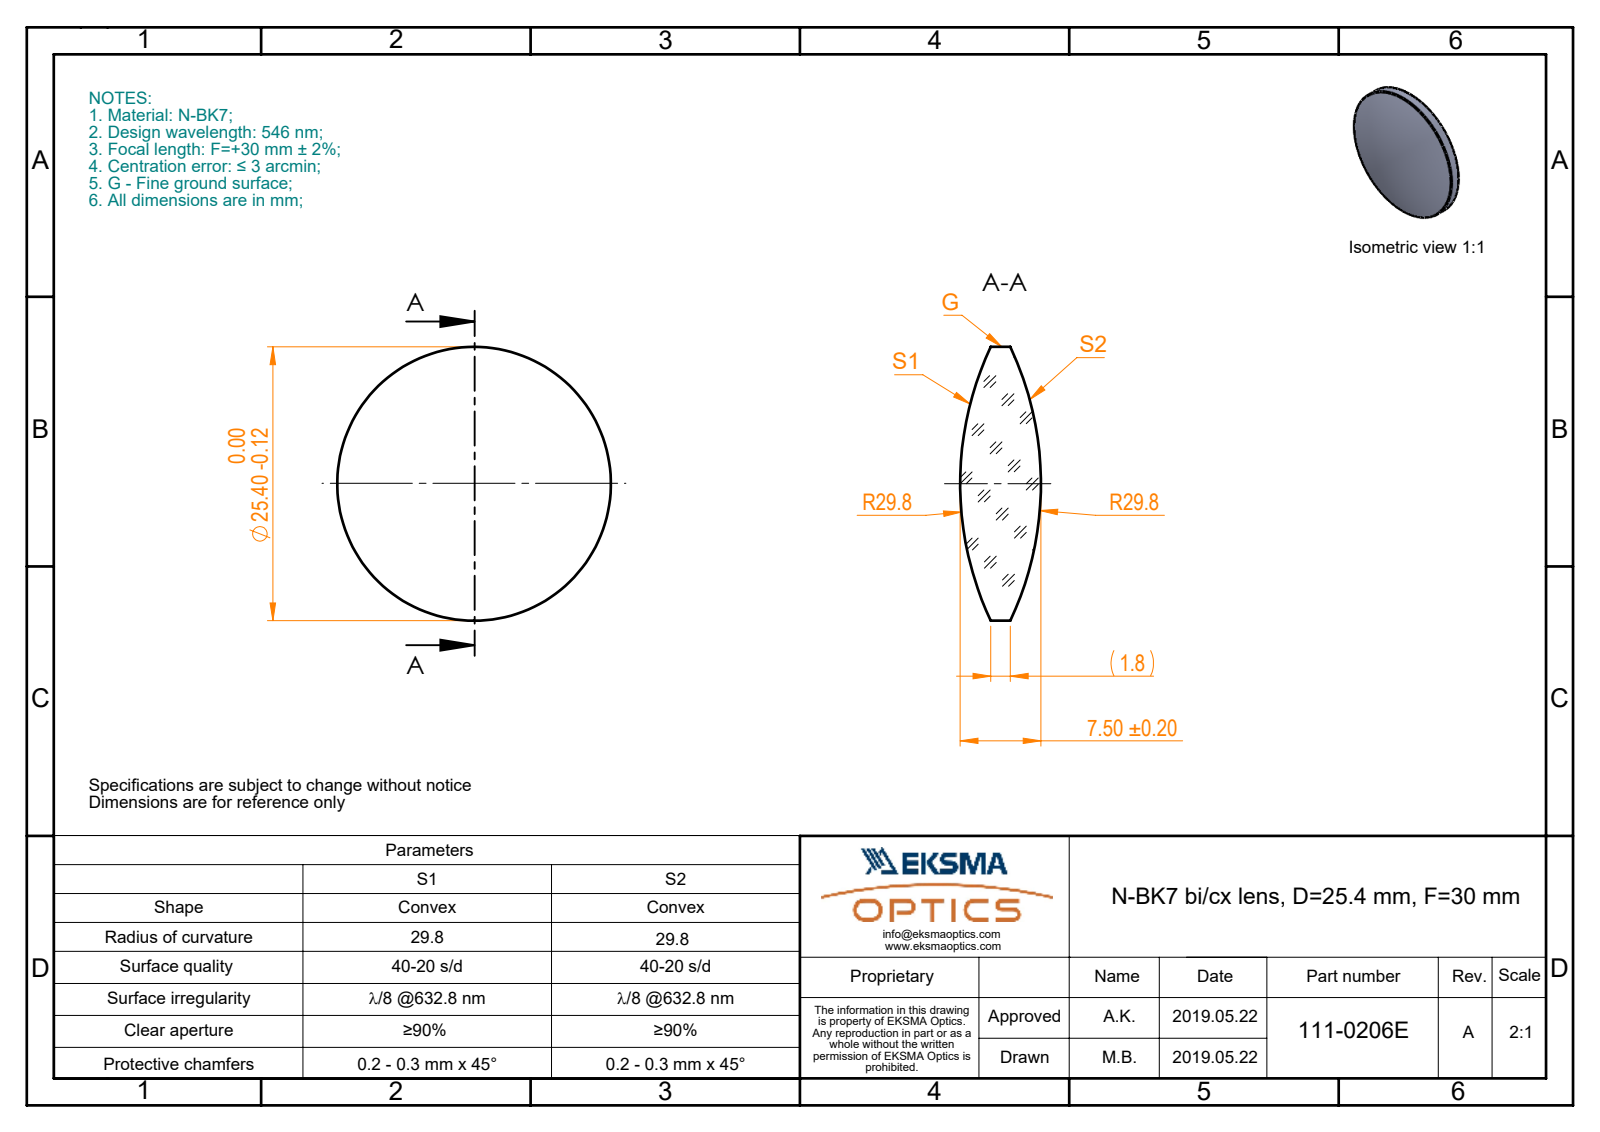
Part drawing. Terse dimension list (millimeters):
name: 111-0206E BK7 bi-cx 25.4 F30
written by: SolidWorks 2017 (CONFIG_CONTROL_DESIGN)
unit: mm
bodies: 1 solid, 6 faces (0 planar, 2 cylindrical, 4 other)
size: 25.4 × 25.4 × 7.5
volume: 2 384 mm³; area: 1 209 mm²
bosses: 1× ⌀25.4
